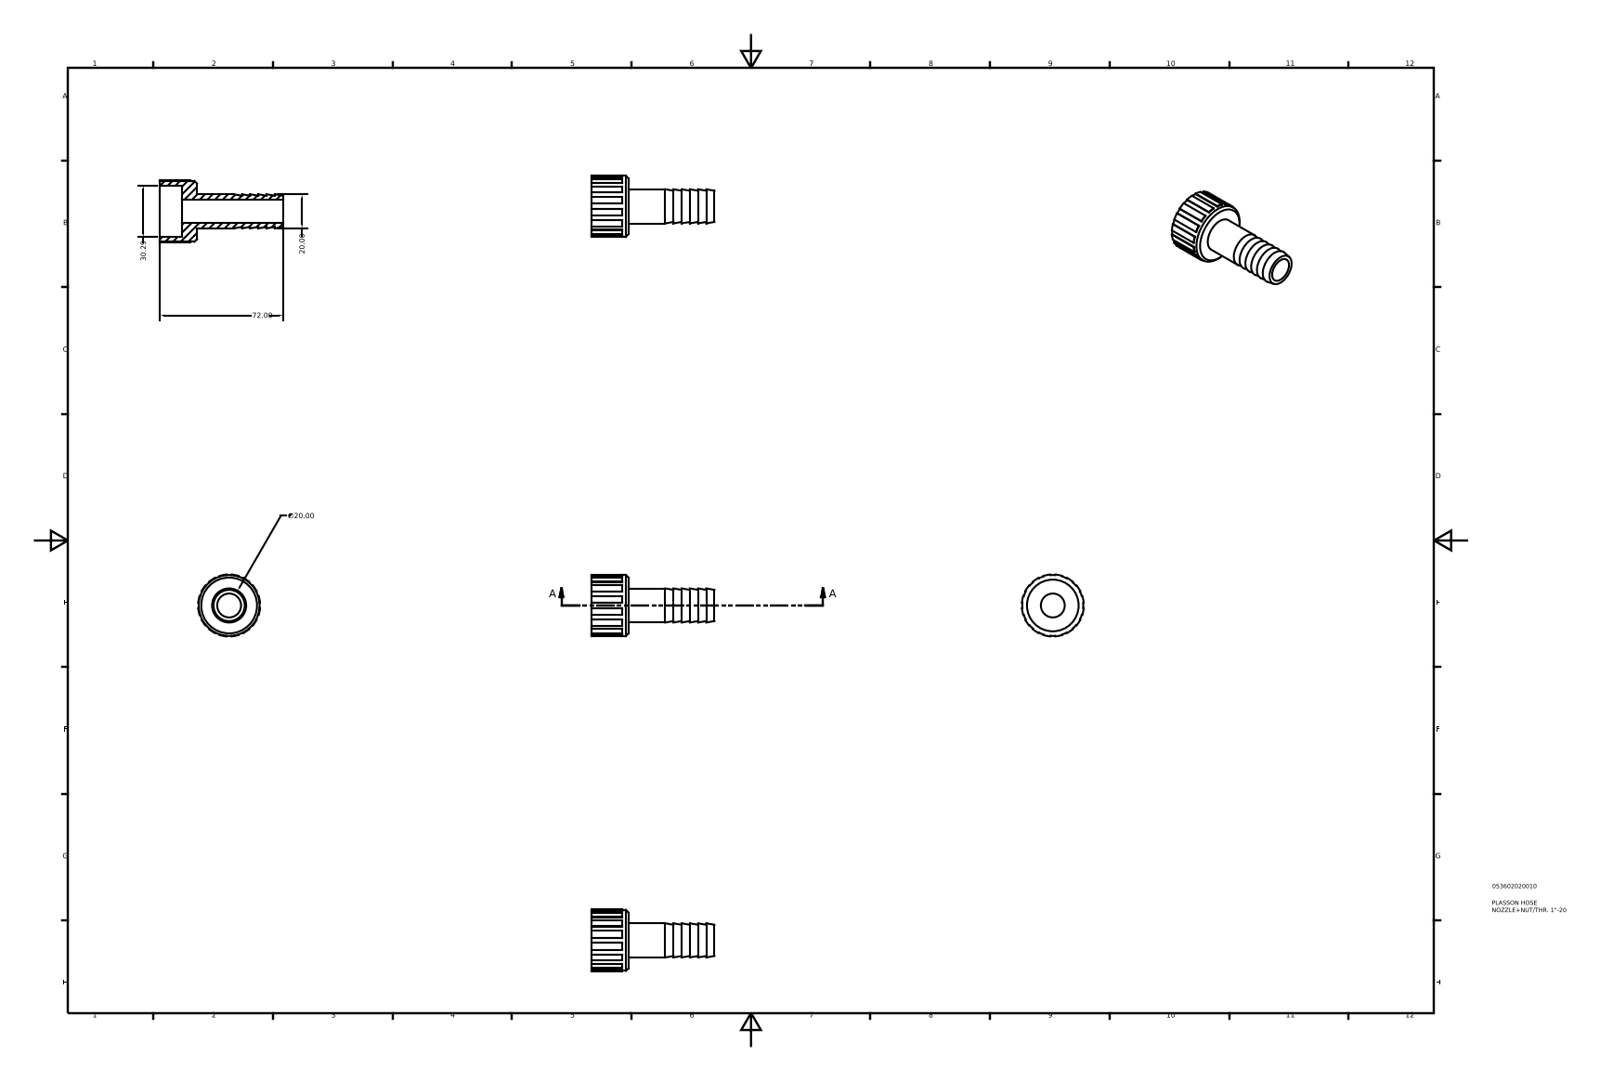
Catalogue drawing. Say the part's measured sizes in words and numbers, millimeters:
The part is named "053602020010". Its 3-D file was written by "Autodesk Inventor 2015 (AUTOMOTIVE_DESIGN)". It is 1 solid with 84 faces: 57 planar, 20 cylindrical and 7 other. Overall it measures 72 by 36.22 by 36.22 millimeters. Its volume is 18 565 cubic millimeters and its surface area 11 406 square millimeters. Round holes: 1 of diameter 14, 1 of diameter 30.29. Round bosses or shafts: 1 of diameter 35.74, 1 of diameter 20. Partial cylindrical surfaces (rounded edges, fillets, slot ends): 1 of radius 18.18. The main face-to-face distances are 8.64, 12.96, 21.6, 4.8, 9.6, 14.4, 72, 59.04, 50.4, 19.2.
